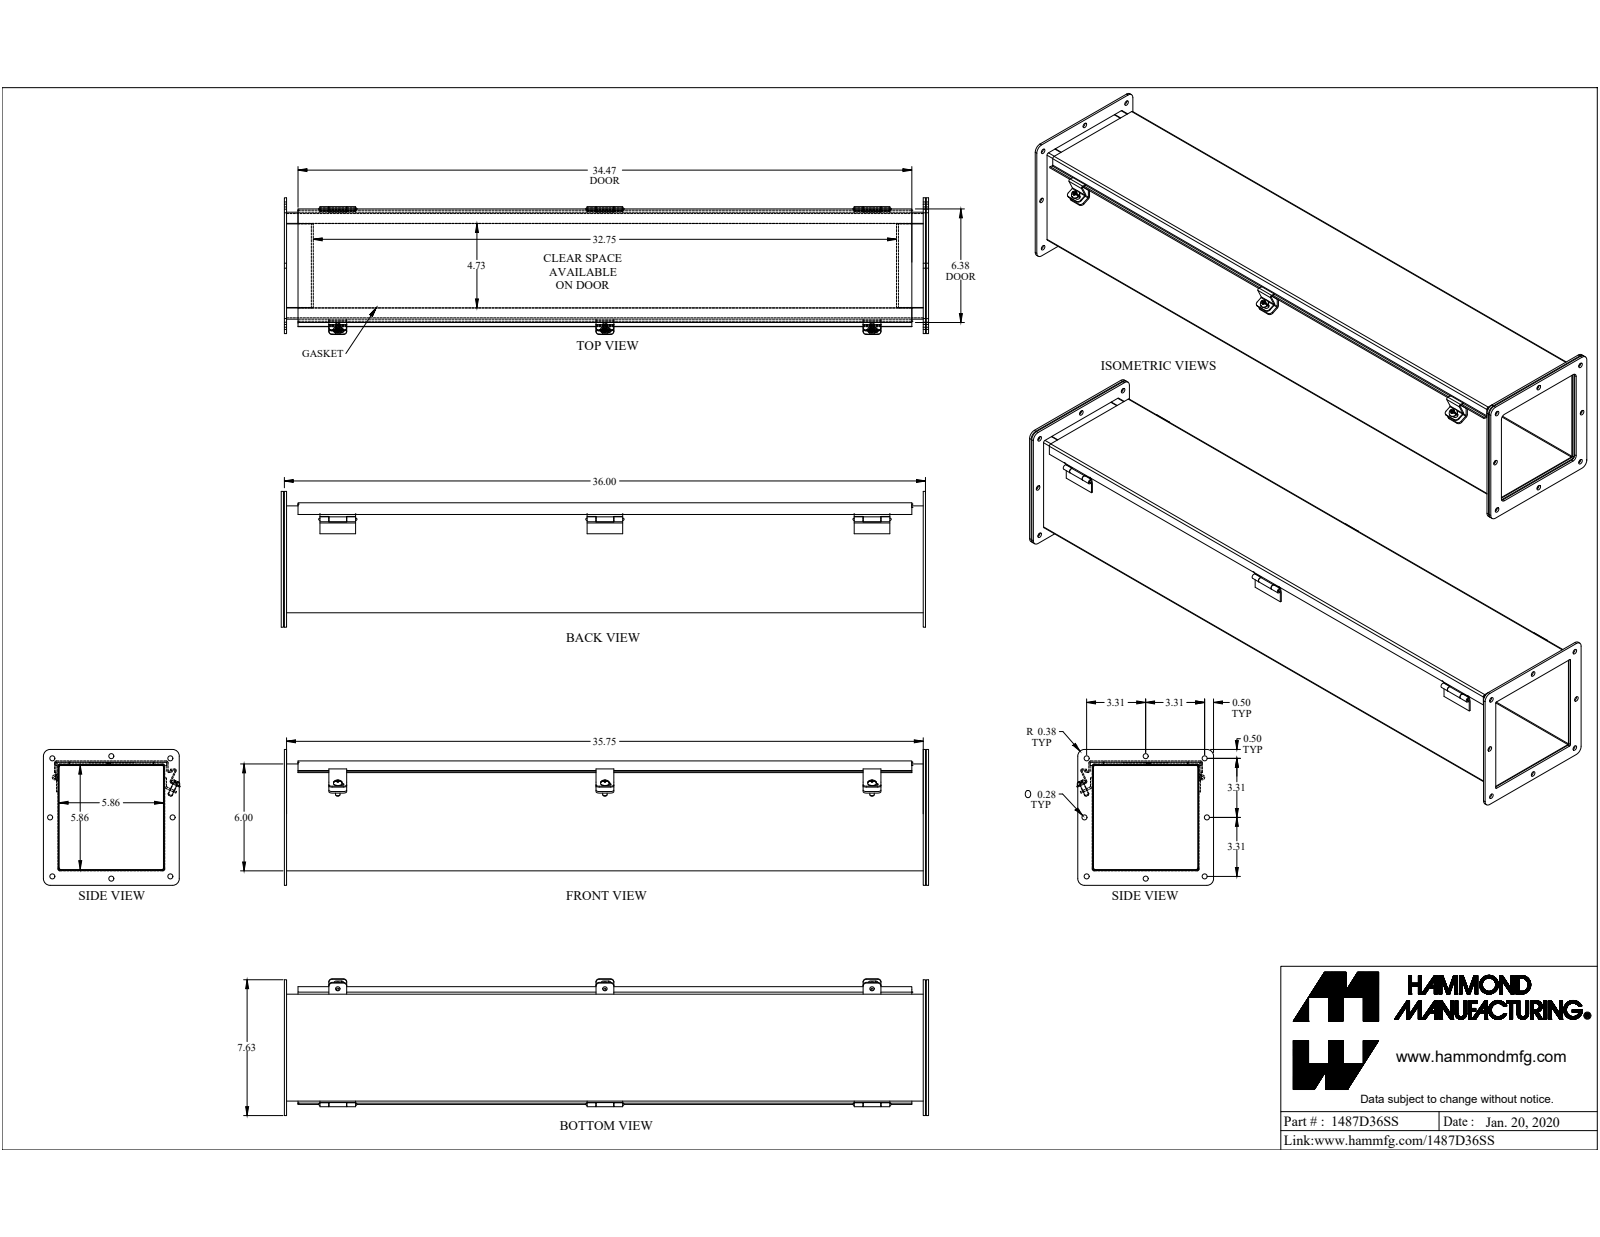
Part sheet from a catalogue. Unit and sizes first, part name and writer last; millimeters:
Units: millimetres
Overall size (bounding box): 928.3 × 195 × 193.7
Round holes (diameter × count): ⌀7.1 ×8, ⌀5.4 ×3, ⌀4.7 ×1, ⌀5 ×1, ⌀6.6 ×1, ⌀8.9 ×1
Round bosses / shafts (diameter × count): ⌀6.4 ×4, ⌀12.2 ×3, ⌀12.7 ×1, ⌀8.6 ×1, ⌀4.6 ×1
Partial cylindrical surfaces — rounded edges, fillets, slot ends (radius × count): R4.8 ×12, R9.5 ×8, R0.9 ×7, R2.7 ×7, R0.5 ×6, R0.8 ×6, R3.6 ×6, R1.6 ×4
Main face-to-face distances: 1.8, 150.6, 154.9, 152.4, 148.7, 156.8, 153.1, 4.7, 4.4, 6.6
Hole centre spacings: 191, 84.2, 84.2, 123.5, 123.5, 168.3, 168.3, 238
Volume: 1 478 000 mm³ · Surface area: 1 485 000 mm²
Bodies: 33 solids, 674 faces (429 planar, 184 cylindrical, 61 other)
Part name (STEP PRODUCT): 1487D36SS
STEP written by: SolidWorks 2019 (CONFIG_CONTROL_DESIGN)
